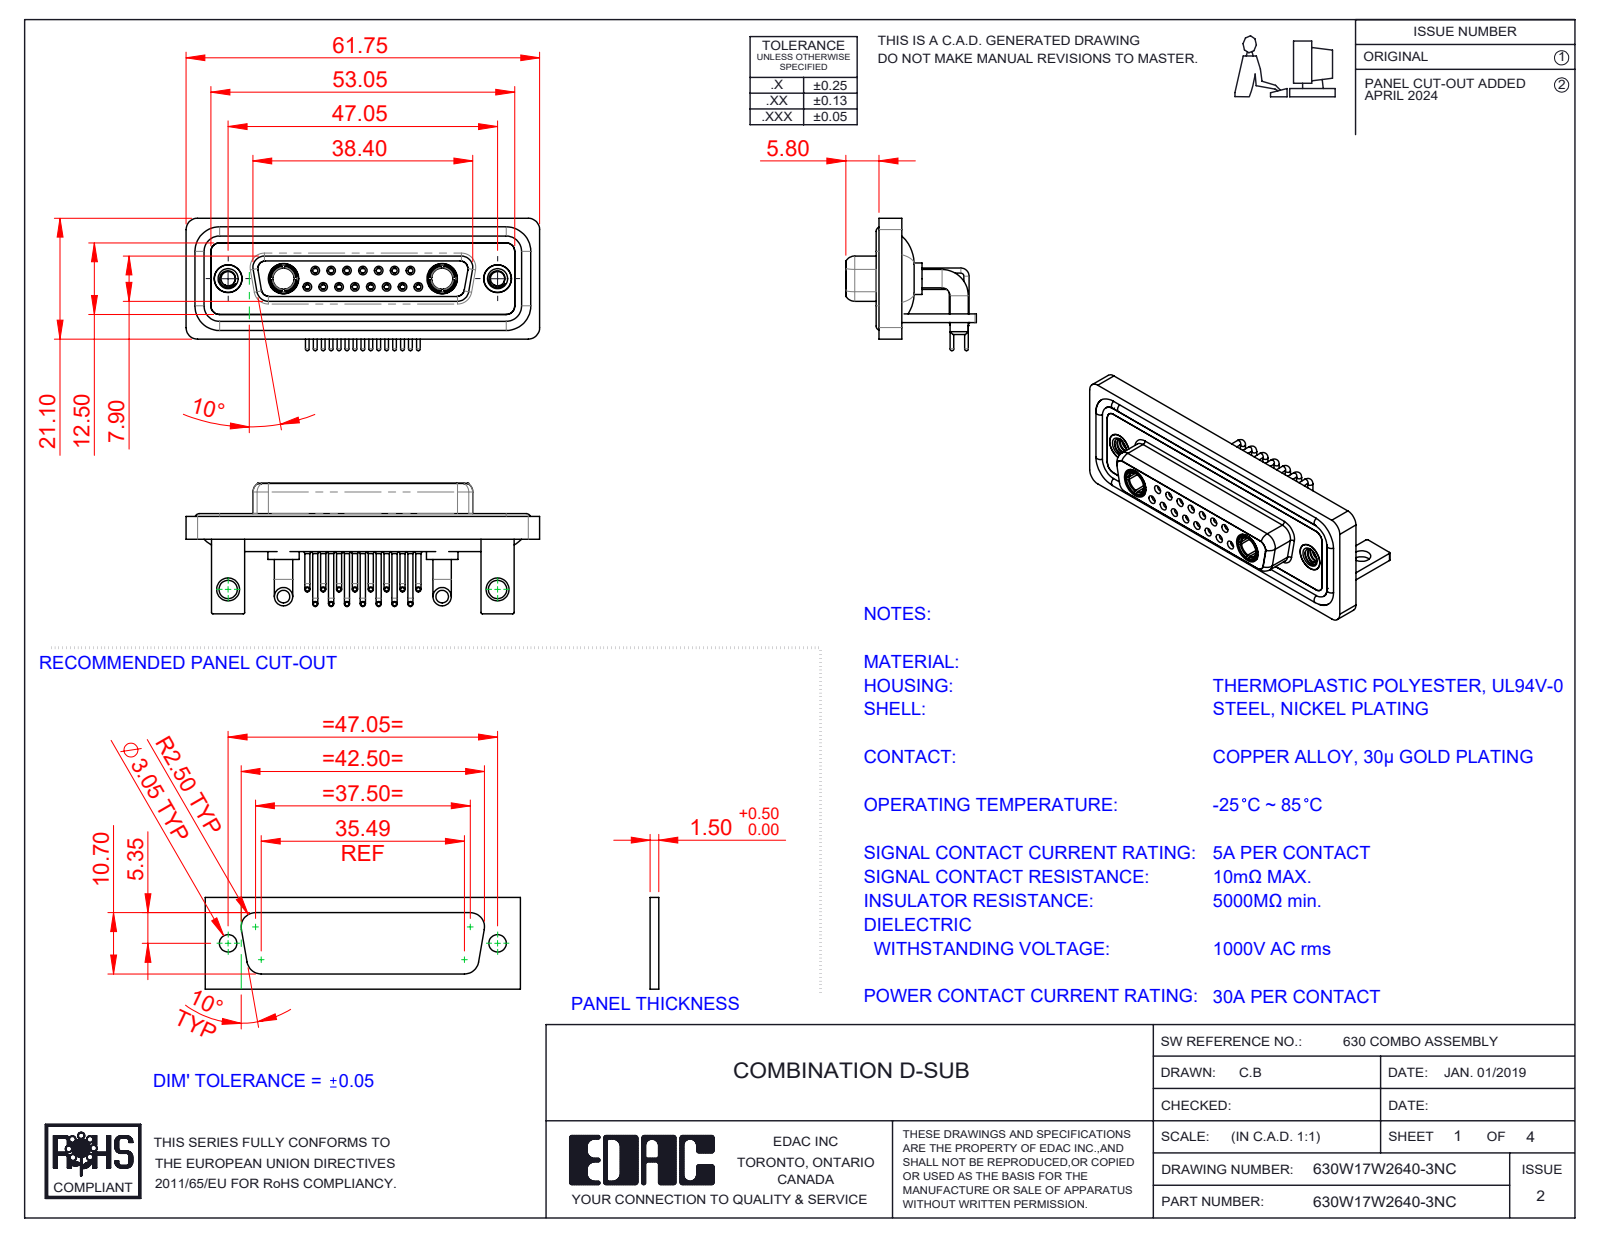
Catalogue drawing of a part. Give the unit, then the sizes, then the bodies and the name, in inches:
Units: inches
Overall size (bounding box): 2.431 × 0.91 × 0.898
Round holes (diameter × count): ⌀0.035 ×15, ⌀0.043 ×15, ⌀0.059 ×15, ⌀0.079 ×15, ⌀0.063 ×8, ⌀0.067 ×7, ⌀0.191 ×4, ⌀0.098 ×2, ⌀0.126 ×2, ⌀0.146 ×2, ⌀0.157 ×2, ⌀0.159 ×2
Round bosses / shafts (diameter × count): ⌀0.035 ×15, ⌀0.026 ×15, ⌀0.063 ×11, ⌀0.126 ×4, ⌀0.217 ×2, ⌀0.205 ×2, ⌀0.195 ×2, ⌀0.195 ×2
Partial cylindrical surfaces — rounded edges, fillets, slot ends (radius × count): R0.079 ×19, R0.059 ×18, R0.01 ×16, R0.053 ×8, R0.063 ×8, R0.02 ×5, R0.024 ×4, R0.026 ×4
Main face-to-face distances: 0.016, 0.071, 0.114, 0.146, 0.059, 0.161, 0.043, 0.055, 0.063, 0.122
Hole centre spacings: 0.124, 0.109, 0.218, 0.327, 0.198, 0.295, 0.436, 0.198
Volume: 0.543 in³ · Surface area: 23.72 in²
Bodies: 28 solids, 1379 faces (408 planar, 605 cylindrical, 366 other)
Part name (STEP PRODUCT): 630Combo Shell Rear_25 Contacts; 630Combo Waterproof Housing_25 Contacts; 630Combo Shell Front_25 Contacts; 630Combo Contact Row 1_50 Contacts (+6 more)
STEP written by: SolidWorks 2023 (CONFIG_CONTROL_DESIGN)
